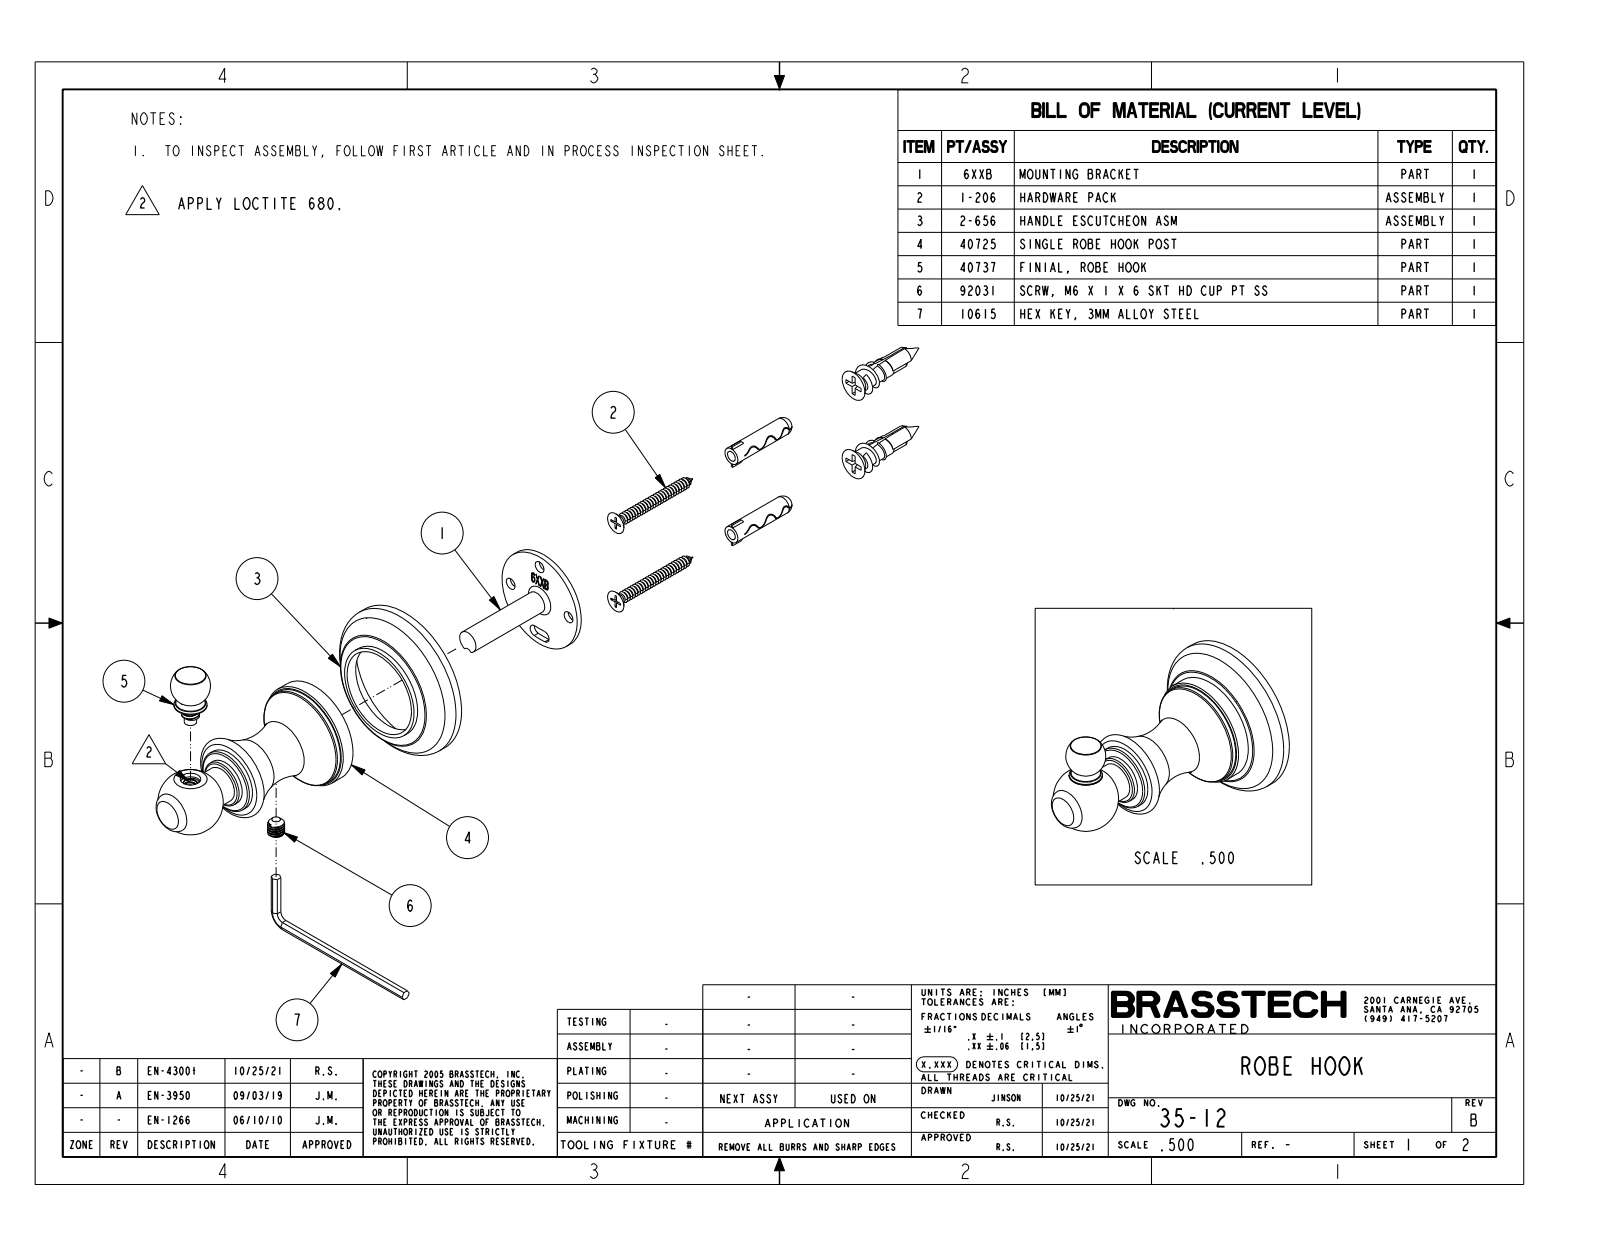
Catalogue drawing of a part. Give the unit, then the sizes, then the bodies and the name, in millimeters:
Units: millimetres
Overall size (bounding box): 84.6 × 55.9 × 55.9
Round bosses / shafts (diameter × count): ⌀55.9 ×1, ⌀37.8 ×1, ⌀37.5 ×1, ⌀36.1 ×1, ⌀22.9 ×1, ⌀16.8 ×1, ⌀13.1 ×1, ⌀11.6 ×1
Main face-to-face distances: 10.9, 2, 53.4, 42.5, 55.4, 44.5, 57.5, 46.5, 4.1, 16.6
Volume: 55 450 mm³ · Surface area: 11 860 mm²
Bodies: 1 solid, 64 faces (8 planar, 16 cylindrical, 40 other)
Part name (STEP PRODUCT): 35-12
STEP written by: CREO PARAMETRIC BY PTC INC, 2018400 (CONFIG_CONTROL_DESIGN)
